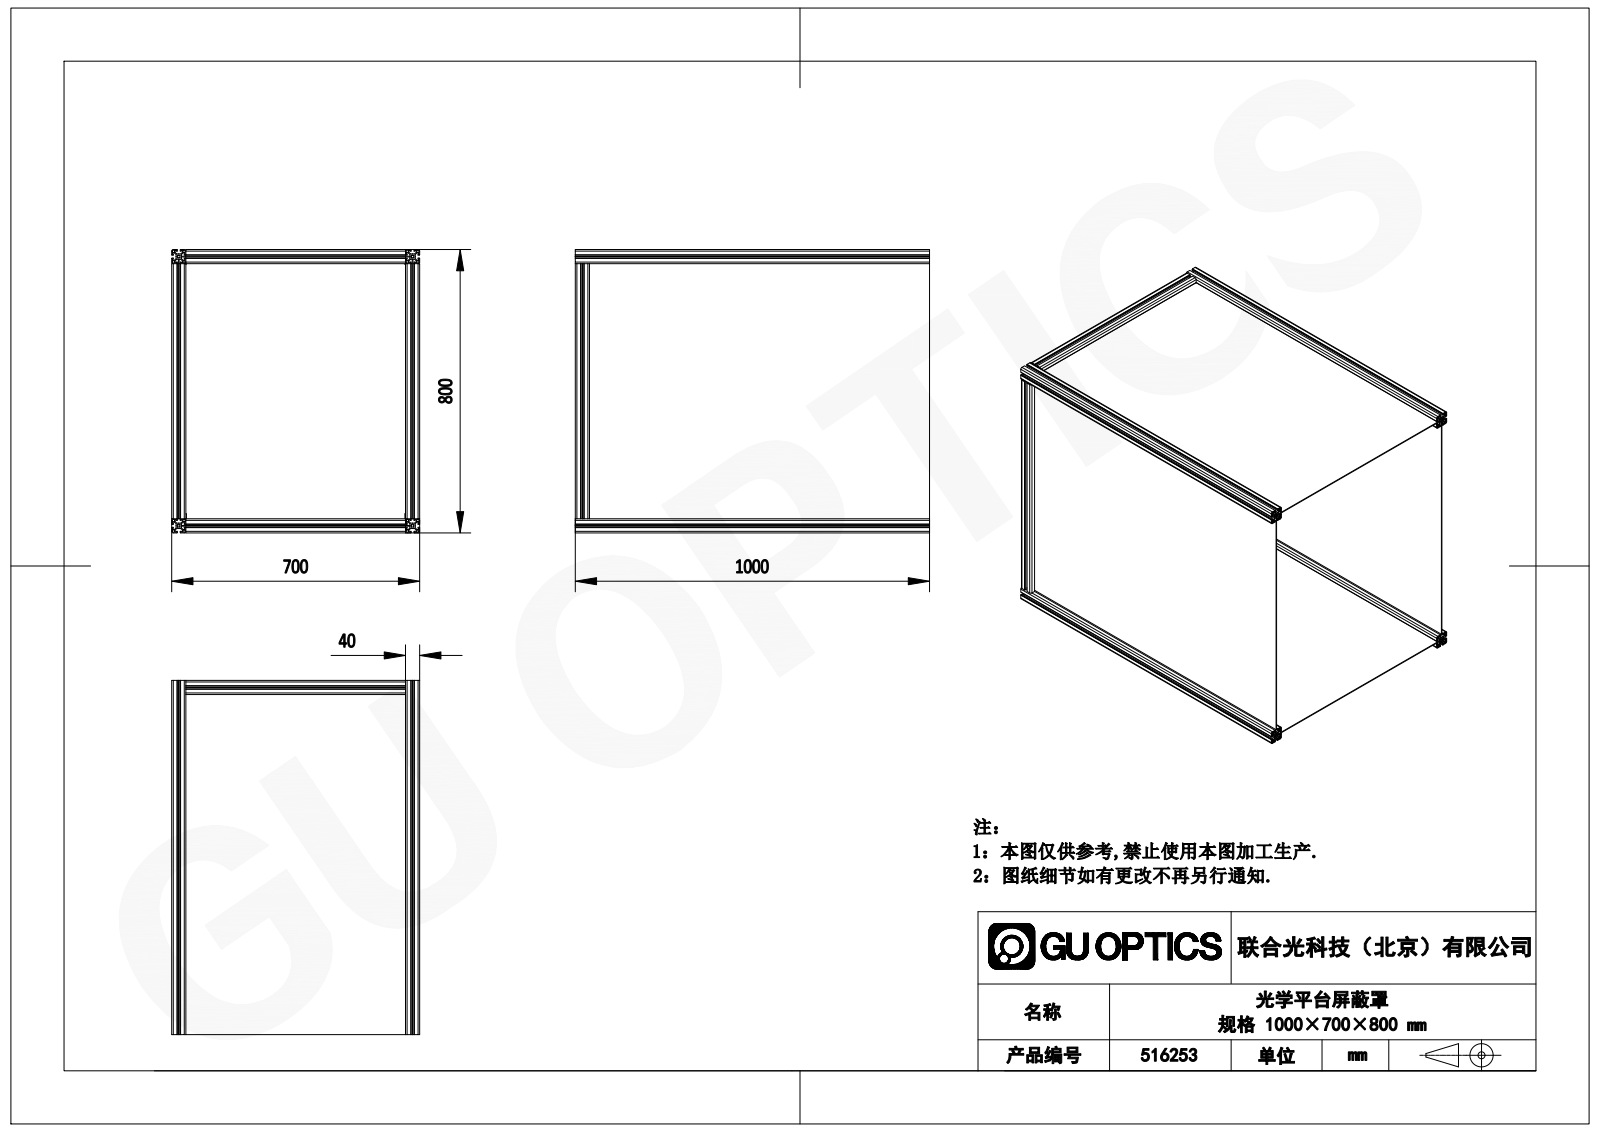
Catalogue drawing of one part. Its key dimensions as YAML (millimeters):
part_name: "光学平台屏蔽罩面板_644_732; 光学平台屏蔽罩边框_620; 光学平台屏蔽罩面板_732_972; 光学平台屏蔽罩边框_1000 (+3 more)"
step_written_by: "SolidWorks 2020 (CONFIG_CONTROL_DESIGN)"
units: millimeters
bodies: {solids: 13, faces: 1230, planar: 950, cylindrical: 280, other: 0}
overall_size: [1000, 800, 700]
volume: 10290000
surface_area: 9619000
partial_cylinders:
  - {radius: 0.5, count: 64}
  - {radius: 1, count: 64}
  - {radius: 0.75, count: 32}
  - {radius: 2.5, count: 32}
  - {radius: 4.5, count: 32}
  - {radius: 3.4, count: 8}
face_to_face_distances: [2, 660, 760, 662, 658, 762, 758, 19, 21, 8.2]
